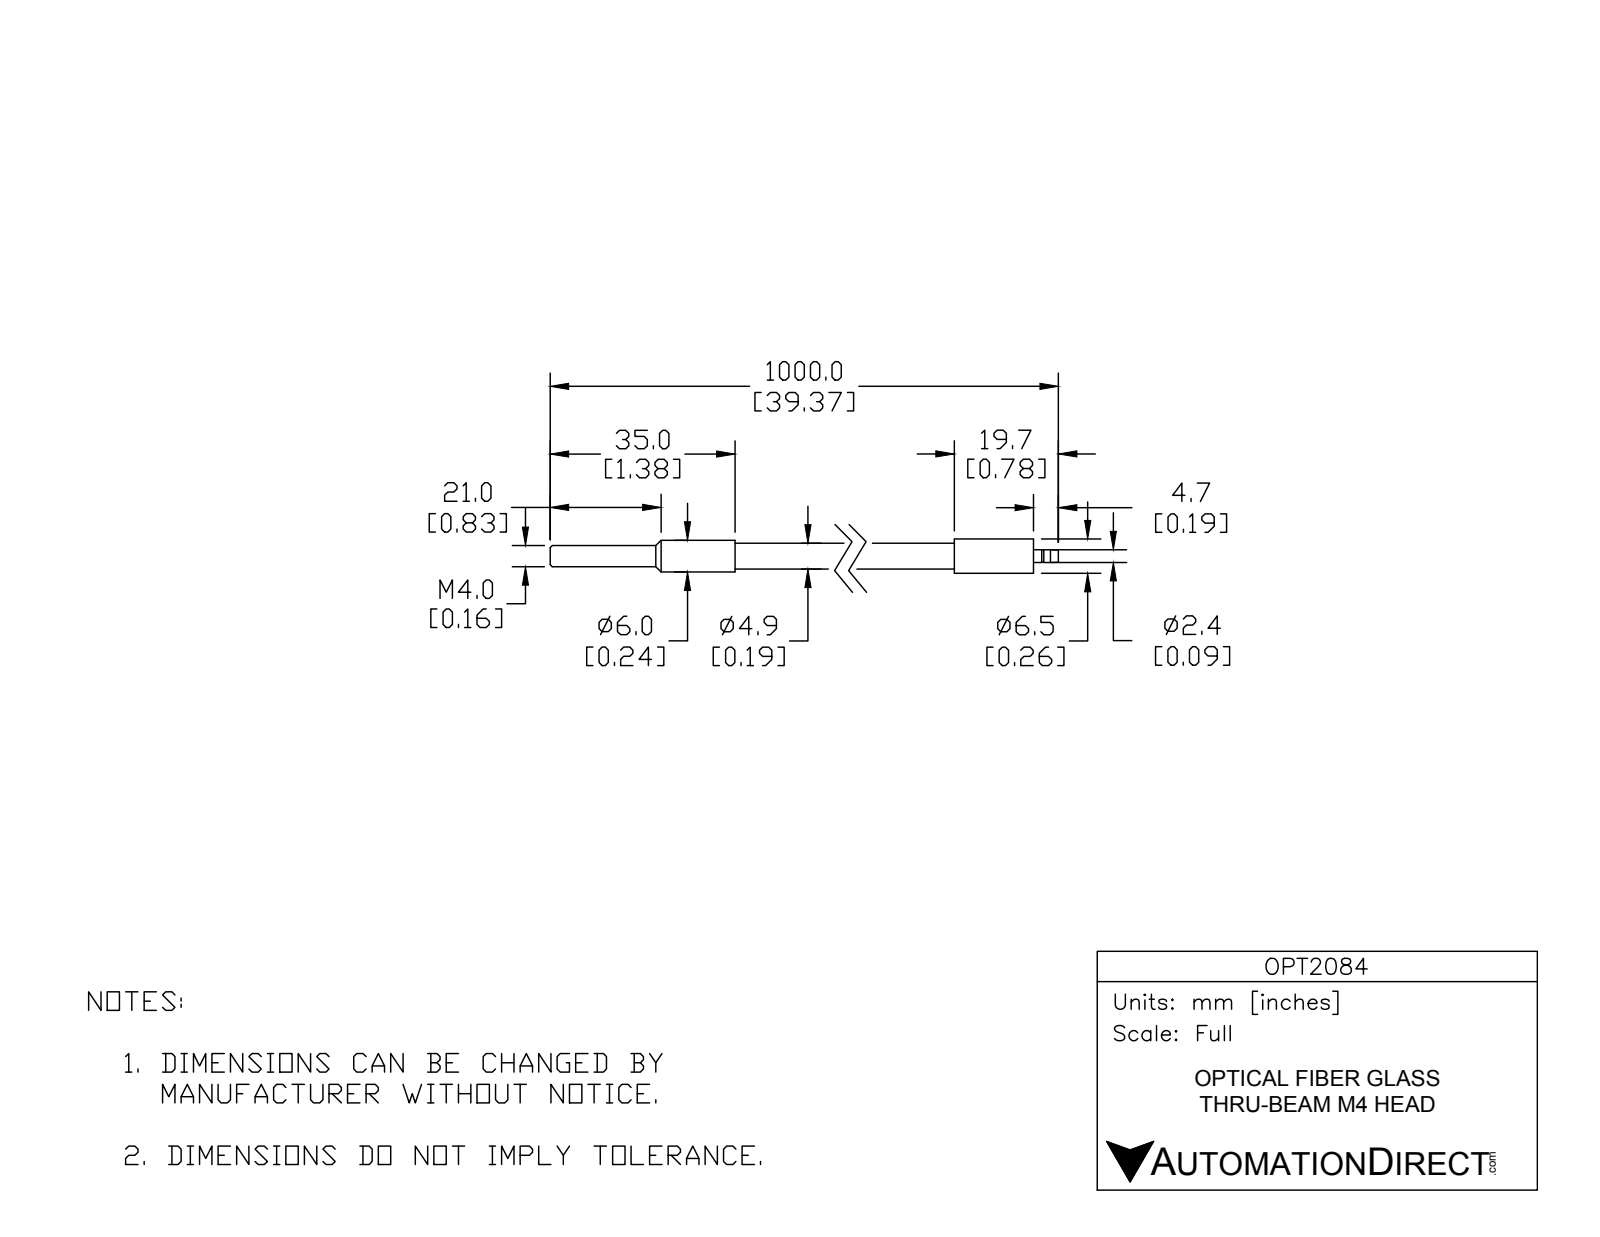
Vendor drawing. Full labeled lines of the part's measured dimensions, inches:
Part name (STEP PRODUCT): OPT2084
STEP written by: SolidWorks 2014 (AUTOMOTIVE_DESIGN)
Units: inches
Bodies: 1 solid, 27 faces (5 planar, 12 cylindrical, 10 other)
Overall size (bounding box): 39.37 × 0.256 × 0.256
Volume: 1.16 in³ · Surface area: 24.02 in²
Round bosses / shafts (diameter × count): ⌀0.256 ×1, ⌀0.236 ×1, ⌀0.193 ×1, ⌀0.157 ×1, ⌀0.094 ×1
Main face-to-face distances: 0.591, 37.217, 37.807, 1.378, 38.594, 39.185, 39.37, 37.992, 0.776, 0.185
